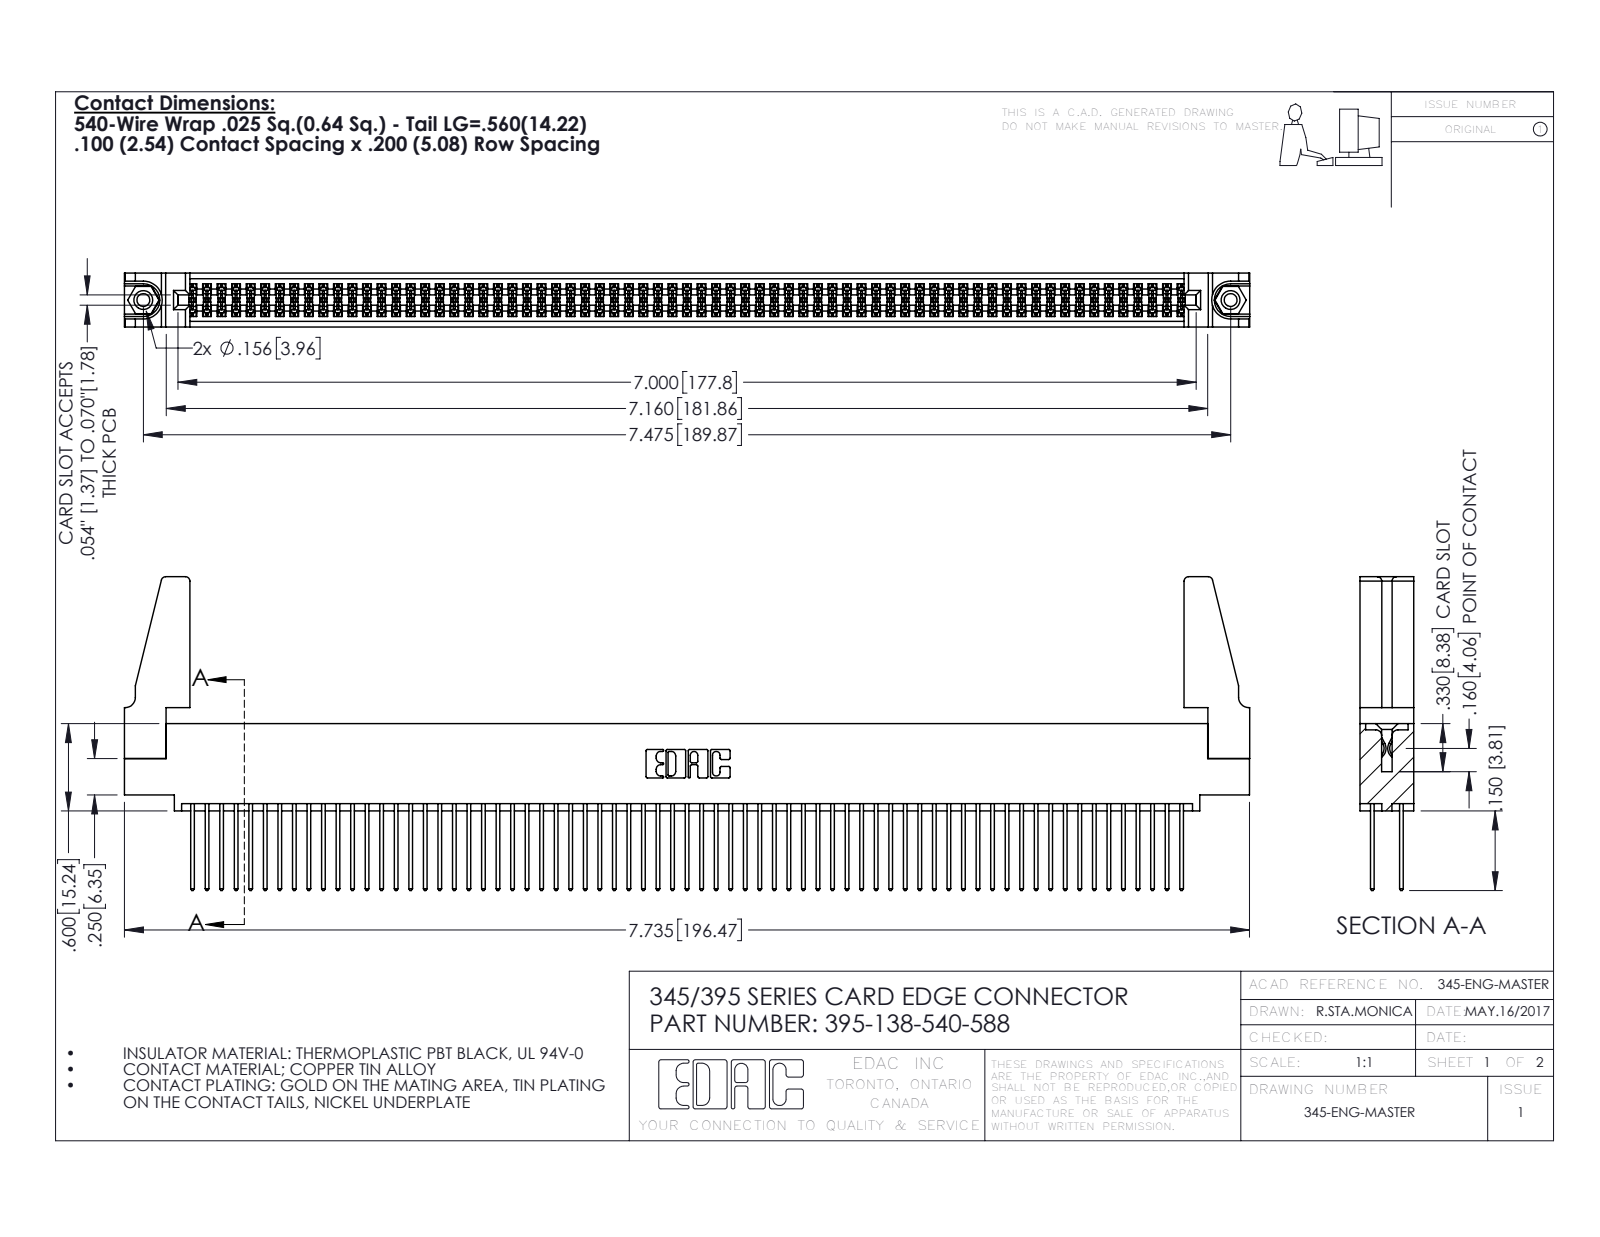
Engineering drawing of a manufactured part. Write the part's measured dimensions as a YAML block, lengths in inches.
part_name: "345 Part_0.110 Offset - 0.156 Dia-TH; 345-250-001_345-250-001-102; 345-292-001_345-293-140; 345-220-078_345-220-088 (+1 more)"
step_written_by: "SolidWorks 2016 (CONFIG_CONTROL_DESIGN)"
units: inches
bodies: {solids: 143, faces: 7154, planar: 4710, cylindrical: 2428, other: 16}
overall_size: [7.736, 2.157, 0.37]
volume: 1.406
surface_area: 54.89
round_holes:
  - {diameter: 0.089, count: 2}
  - {diameter: 0.125, count: 2}
  - {diameter: 0.156, count: 2}
  - {diameter: 0.064, count: 1}
round_bosses_or_shafts:
  - {diameter: 0.155, count: 2}
partial_cylinders:
  - {radius: 0.006, count: 207}
  - {radius: 0.01, count: 138}
  - {radius: 0.01, count: 22}
  - {radius: 0.03, count: 8}
  - {radius: 0.007, count: 6}
  - {radius: 0.031, count: 6}
  - {radius: 0.026, count: 3}
  - {radius: 0.014, count: 2}
face_to_face_distances: [0.072, 0.298, 0.098, 0.272, 0.025, 0.2, 0.37, 0.225, 0.175, 0.149]
hole_center_spacings: [0.27, 7.239, 7.475]
